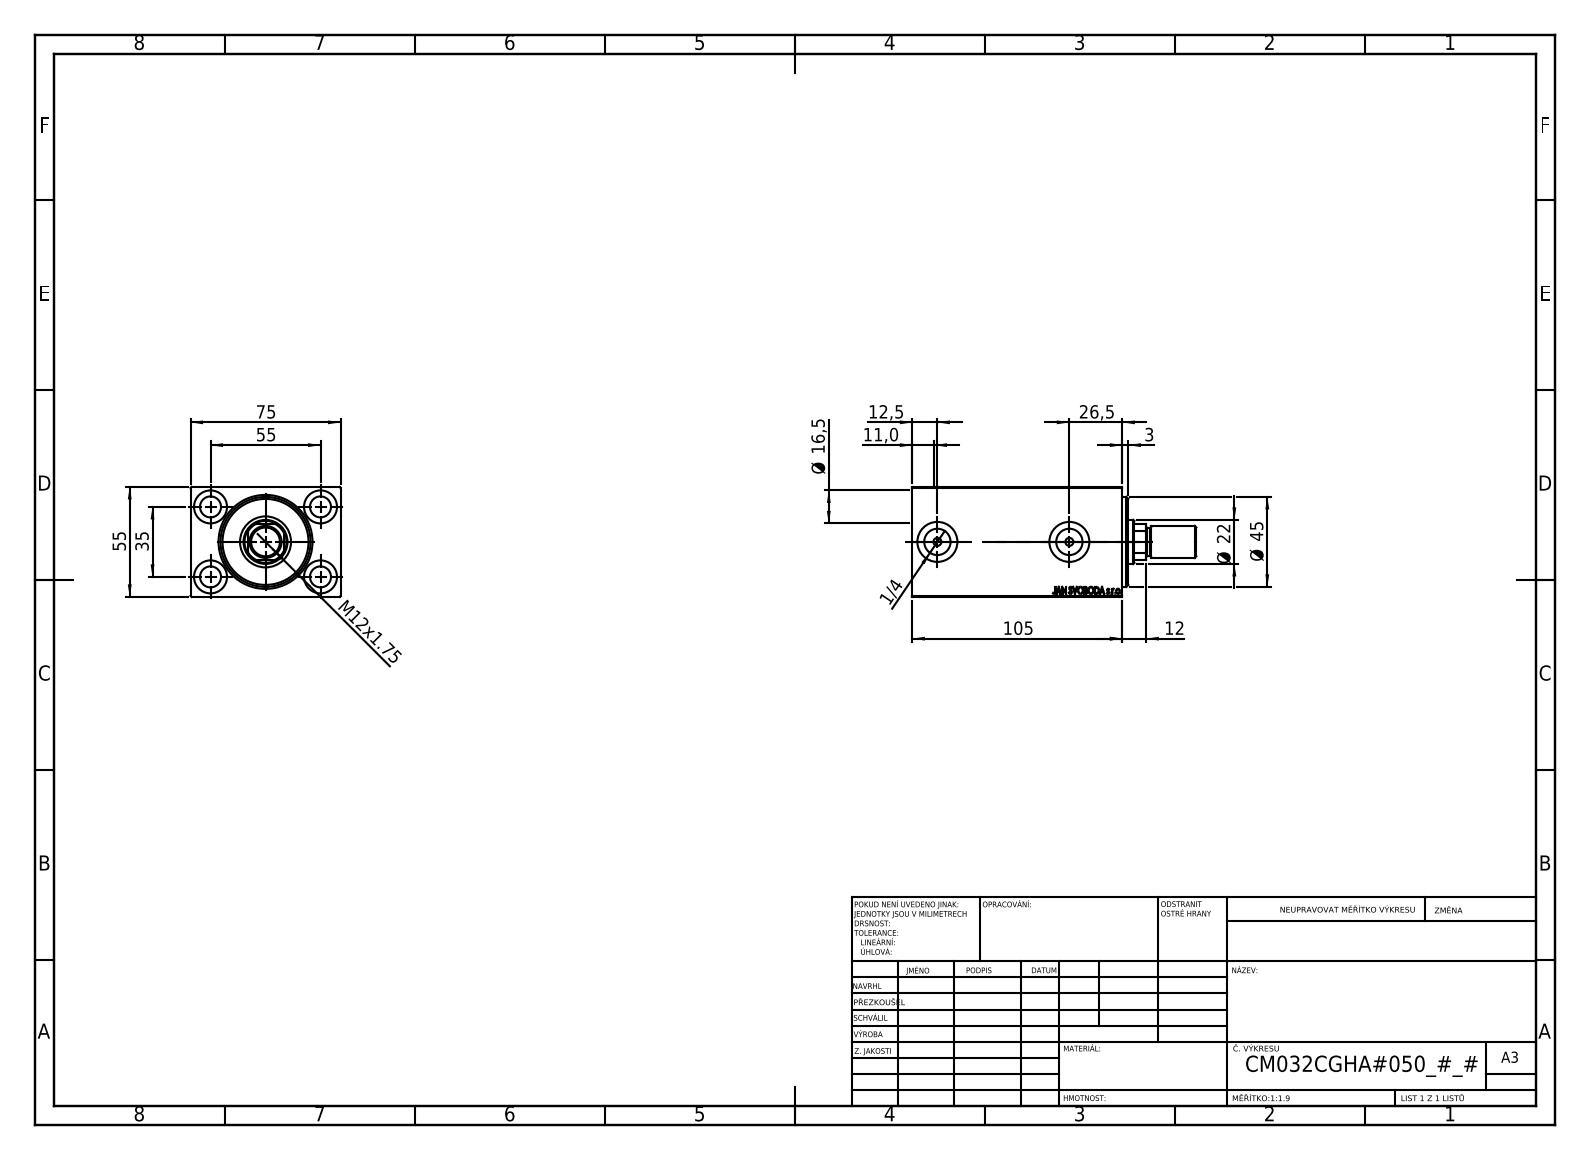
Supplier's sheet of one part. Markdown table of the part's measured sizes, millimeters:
| quantity | value |
| --- | --- |
| part name | V450CM_VC_B; V450CM_MALE_METRIC; V450CM_C_Body; V450CM_C_VCP |
| STEP written by | SolidWorks 2019 (CONFIG_CONTROL_DESIGN) |
| units | millimeters |
| bodies | 4 solids, 875 faces (411 planar, 64 cylindrical, 400 other) |
| overall size | 142 × 75 × 55 |
| volume | 371 210 mm³ |
| surface area | 78 823 mm² |
| round holes (diameter × count) | 10.5 × 5, 16.5 × 4, 4 × 2, 13.16 × 2, 20 × 2, 22 × 1, 25.5 × 1, 32 × 1, 34 × 1, 45 × 1 |
| round bosses / shafts (diameter × count) | 16 × 1, 14 × 1 |
| partial cylindrical surfaces (radius × count) | 10.5 × 1 |
| main face-to-face distances | 55, 75, 10, 95, 105, 100, 5, 90, 83, 11 |
| hole center spacings | 32.6, 35, 55, 65.19, 66 |
